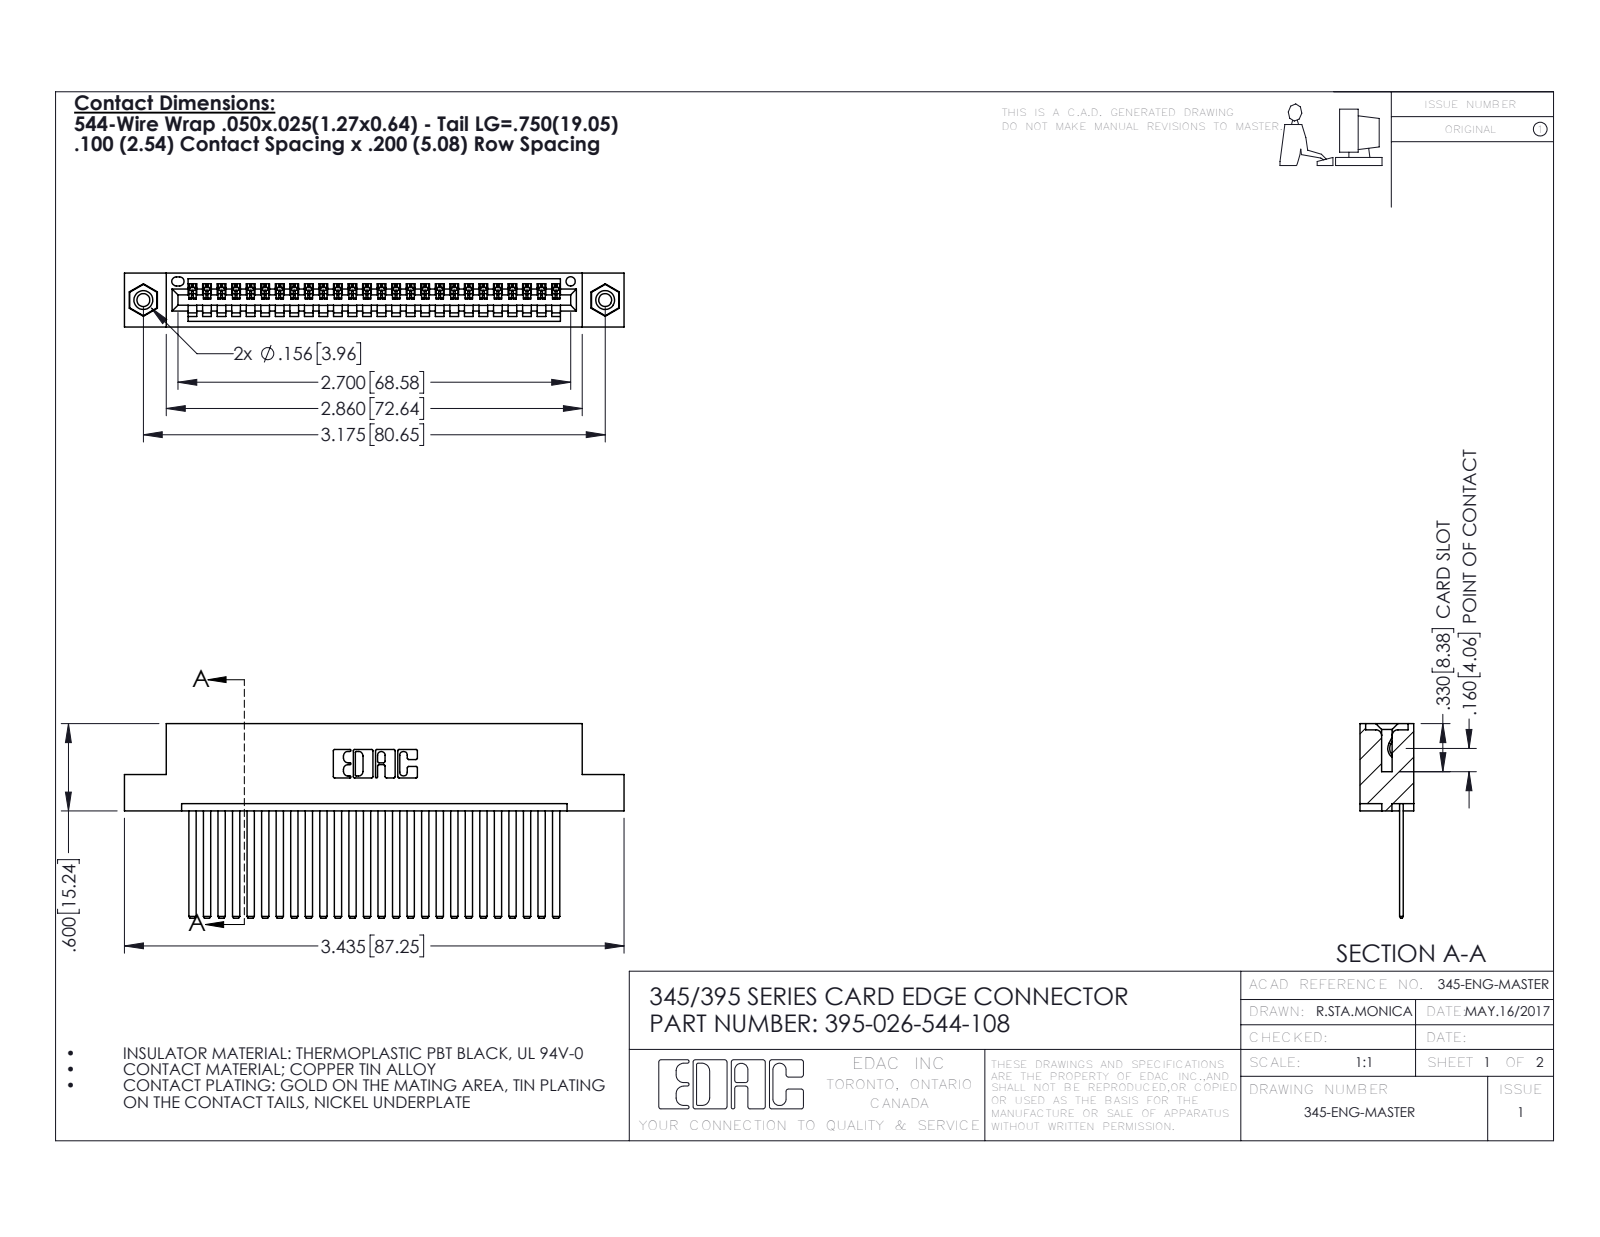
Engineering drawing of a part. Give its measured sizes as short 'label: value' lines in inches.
name: 345-250-001_345-250-003-102; 395-026-544-108; 345-292-001_345-293-144; 345 Part_Flush Mounting Lugs - 0.156 Dia-TI
written by: SolidWorks 2016 (CONFIG_CONTROL_DESIGN)
unit: in
bodies: 29 solids, 1538 faces (1048 planar, 474 cylindrical, 16 other)
size: 3.435 × 1.337 × 0.37
volume: 0.516 in³; area: 18.5 in²
holes: 2× ⌀0.089, 2× ⌀0.125, 2× ⌀0.156, 1× ⌀0.064
bosses: 2× ⌀0.155
rounds: 52× R0.006, 22× R0.01, 6× R0.007, 6× R0.031, 3× R0.026, 2× R0.031, 2× R0.04, 1× R0.014
face distances: 0.072, 0.298, 0.098, 0.025, 0.272, 0.2, 0.37, 0.225, 0.149, 0.072
hole spacings: 0.27, 2.94, 3.175
